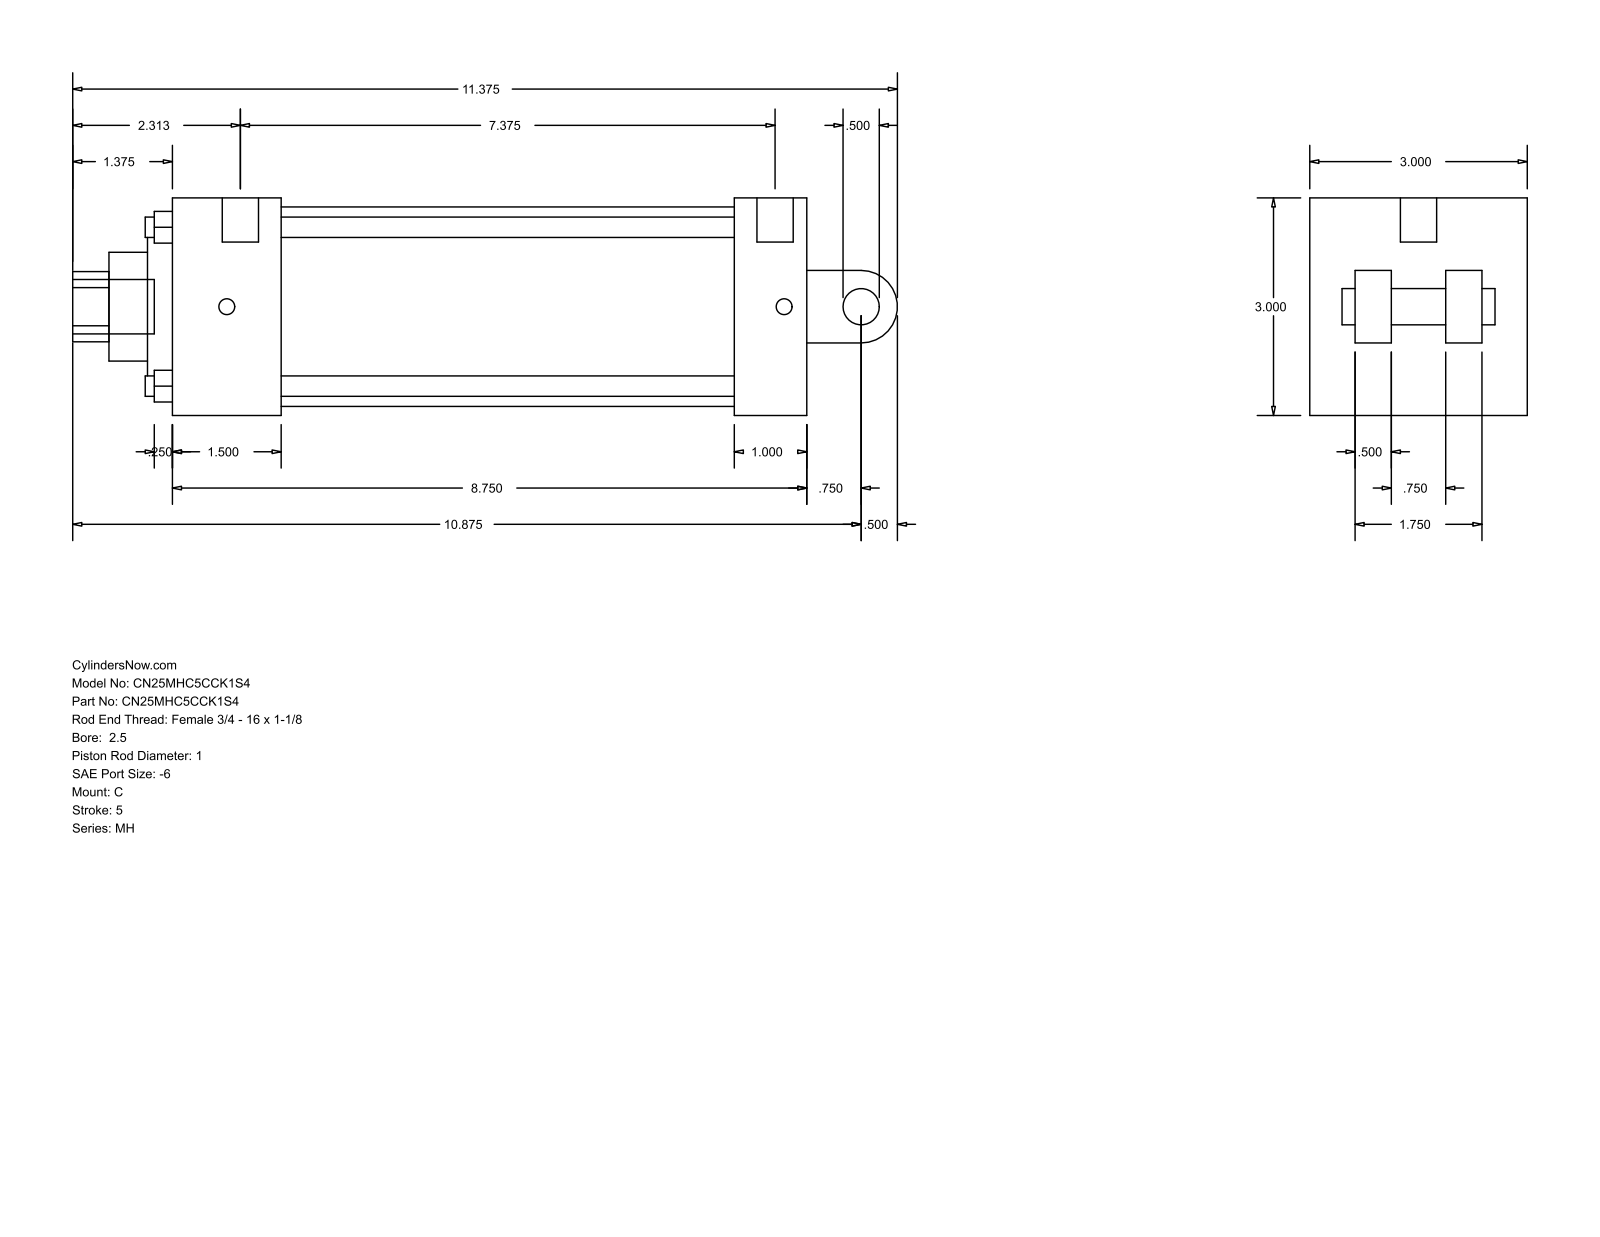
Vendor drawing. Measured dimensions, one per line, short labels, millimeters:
name: MH_C__0250_1
written by: GSSL Pune (CONFIG_CONTROL_DESIGN)
unit: mm
bodies: 0 solids, 101 faces (71 planar, 30 cylindrical, 0 other)
size: 288.93 × 76.2 × 76.2
holes: 4× ⌀7.14, 2× ⌀5.56, 1× ⌀12.7, 1× ⌀25.4, 1× ⌀38.1, 1× ⌀60.33, 1× ⌀69.85
bosses: 2× ⌀12.7, 2× ⌀5.56, 1× ⌀19.05
rounds: 1× R12.29, 1× R12.7
face distances: 76.2, 25.4, 222.26, 15.87, 60.33, 196.86, 38.11, 158.75, 184.15, 12.7
hole spacings: 39.33, 55.62, 78.66, 3.18
